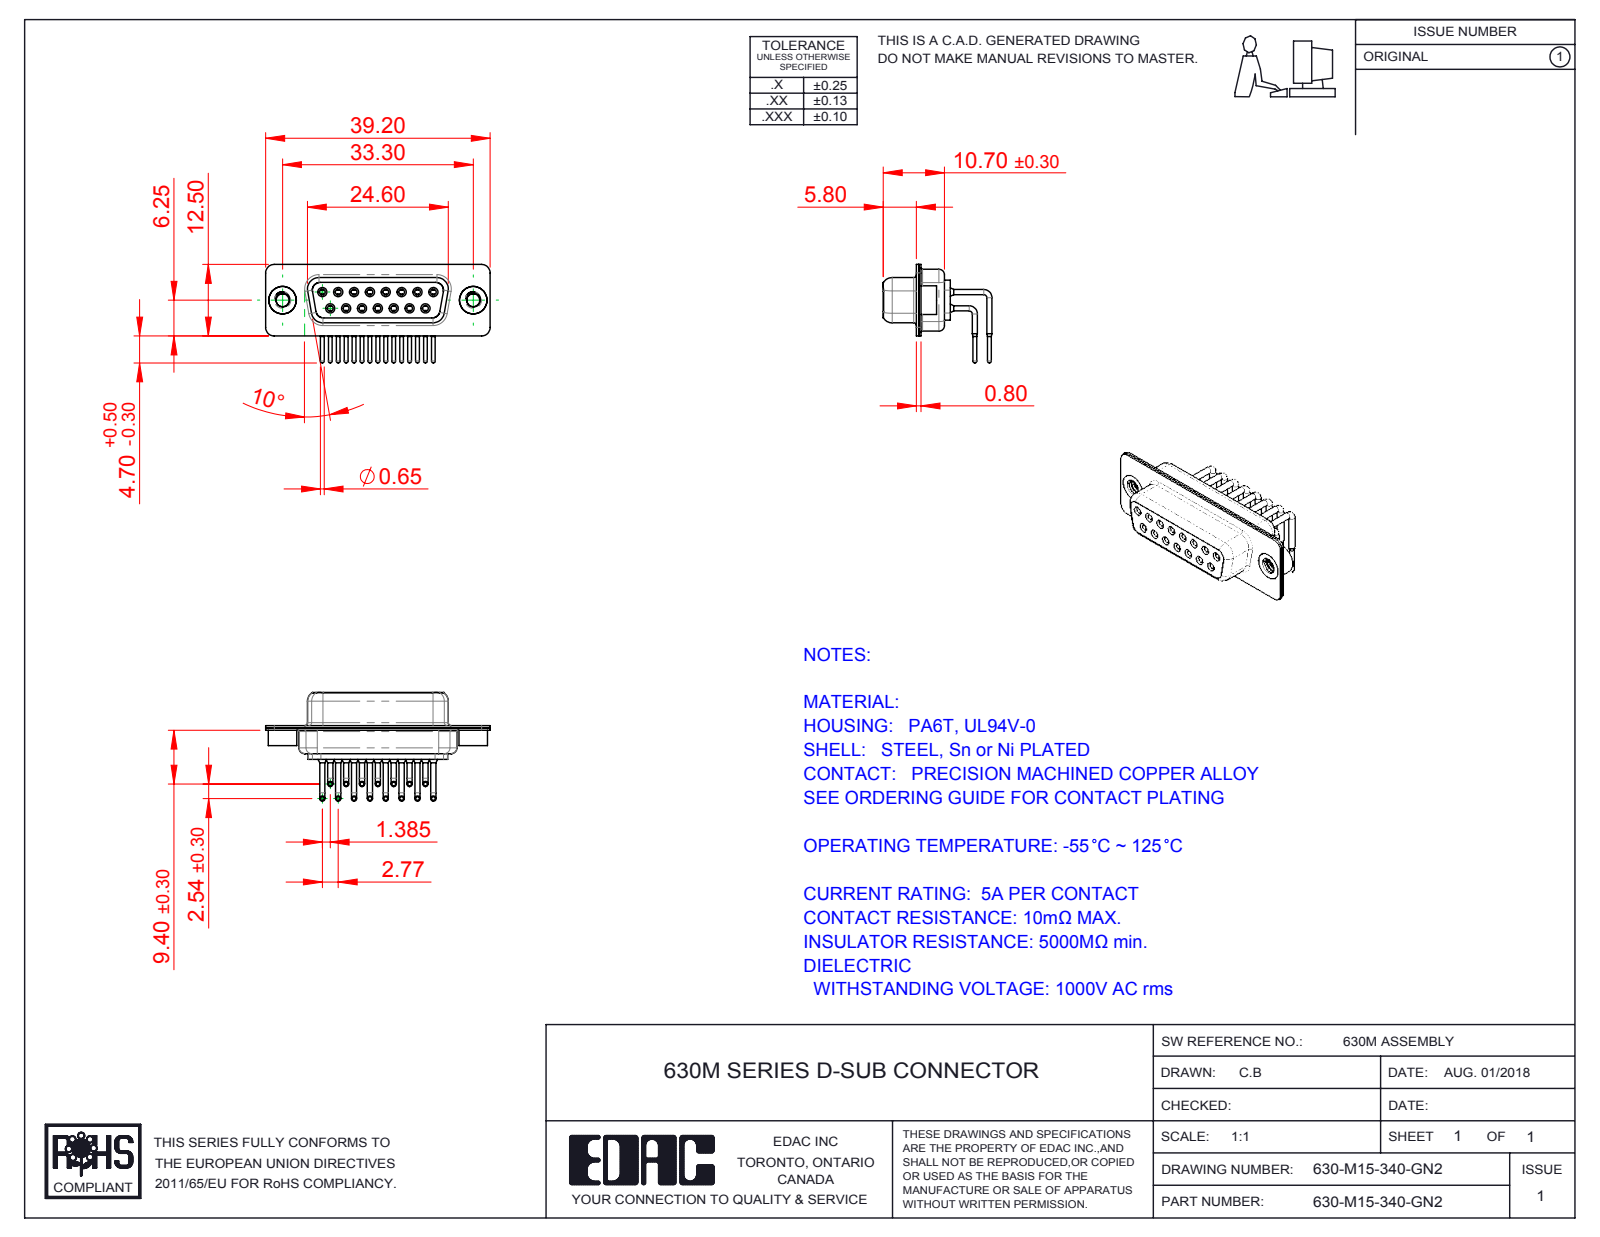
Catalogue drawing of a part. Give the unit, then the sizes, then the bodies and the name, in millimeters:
Units: millimetres
Overall size (bounding box): 39.2 × 18.99 × 17.2
Round holes (diameter × count): ⌀1 ×15, ⌀1.1 ×15, ⌀1.7 ×15, ⌀1.8 ×15, ⌀2 ×15, ⌀2.26 ×2, ⌀4 ×2, ⌀4.8 ×2
Round bosses / shafts (diameter × count): ⌀0.9 ×30, ⌀1.6 ×15, ⌀1.5 ×15, ⌀0.65 ×15, ⌀5 ×2, ⌀4.9 ×2
Partial cylindrical surfaces — rounded edges, fillets, slot ends (radius × count): R1.5 ×16, R2 ×12, R1.35 ×8, R1.6 ×8, R0.25 ×4, R0.5 ×4, R0.6 ×4, R0.65 ×4
Main face-to-face distances: 0.4, 1.45, 8.95, 2.3, 6.2, 0.8, 1.9, 8.5, 0.45, 7.05
Hole centre spacings: 3.16, 2.77, 5.54, 8.31, 11.08, 5.03, 5.04, 7.48
Volume: 2 568 mm³ · Surface area: 6 554 mm²
Bodies: 20 solids, 1074 faces (292 planar, 482 cylindrical, 300 other)
Part name (STEP PRODUCT): 630M Shell Front_15 Contacts; 630-M15-340-GN2; 630M Housing_15 Contacts; 630M Contact Row 2 (+3 more)
STEP written by: SolidWorks 2016 (CONFIG_CONTROL_DESIGN)
